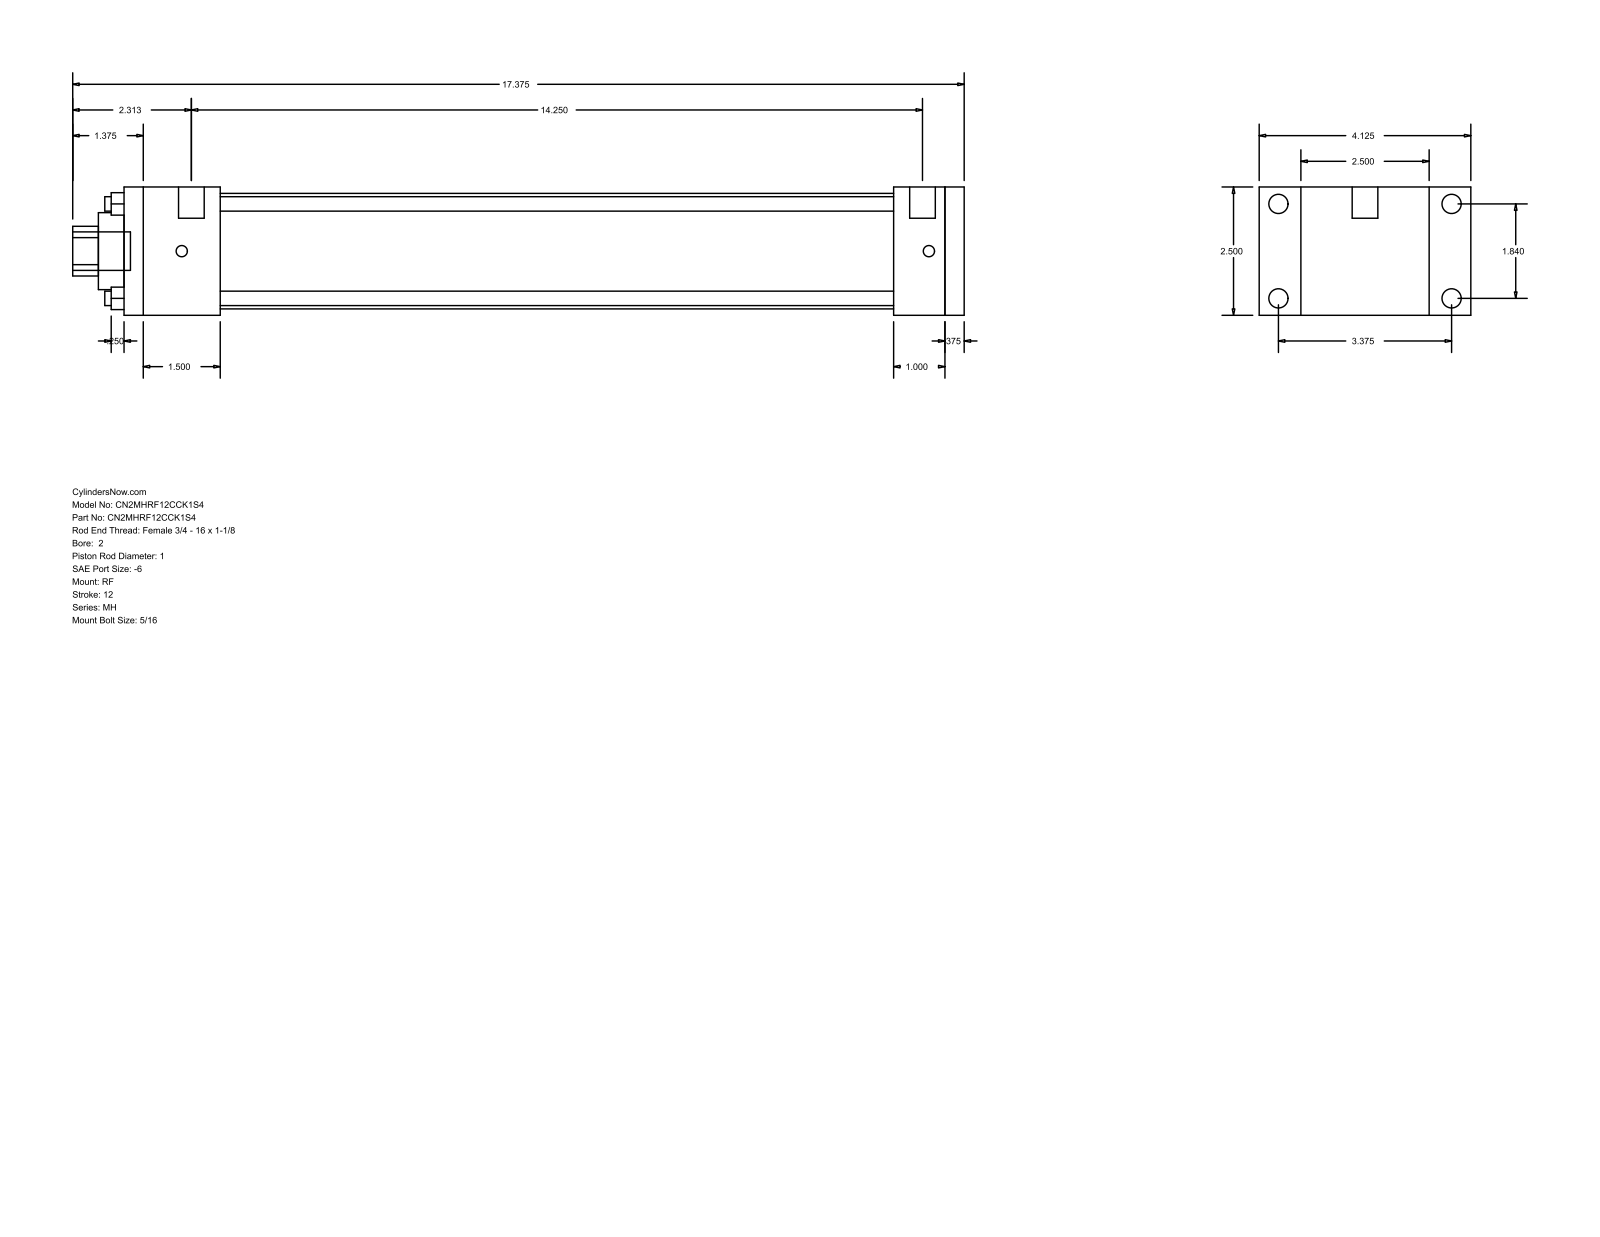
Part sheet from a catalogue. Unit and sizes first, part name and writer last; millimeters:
Units: millimetres
Overall size (bounding box): 441.32 × 104.78 × 63.5
Round holes (diameter × count): ⌀7.14 ×4, ⌀25.4 ×1, ⌀38.1 ×1, ⌀57.15 ×1
Round bosses / shafts (diameter × count): ⌀9.53 ×4, ⌀5.56 ×4, ⌀12.7 ×2, ⌀19.05 ×1
Partial cylindrical surfaces — rounded edges, fillets, slot ends (radius × count): R12.29 ×1
Main face-to-face distances: 63.5, 9.52, 415.92, 406.4, 20.64, 25.4, 47.63, 381, 333.37, 358.77
Hole centre spacings: 33.05, 46.74, 66.1
Bodies: 0 solids, 92 faces (64 planar, 28 cylindrical, 0 other)
Part name (STEP PRODUCT): MH_RF__0200_1
STEP written by: GSSL Pune (CONFIG_CONTROL_DESIGN)
